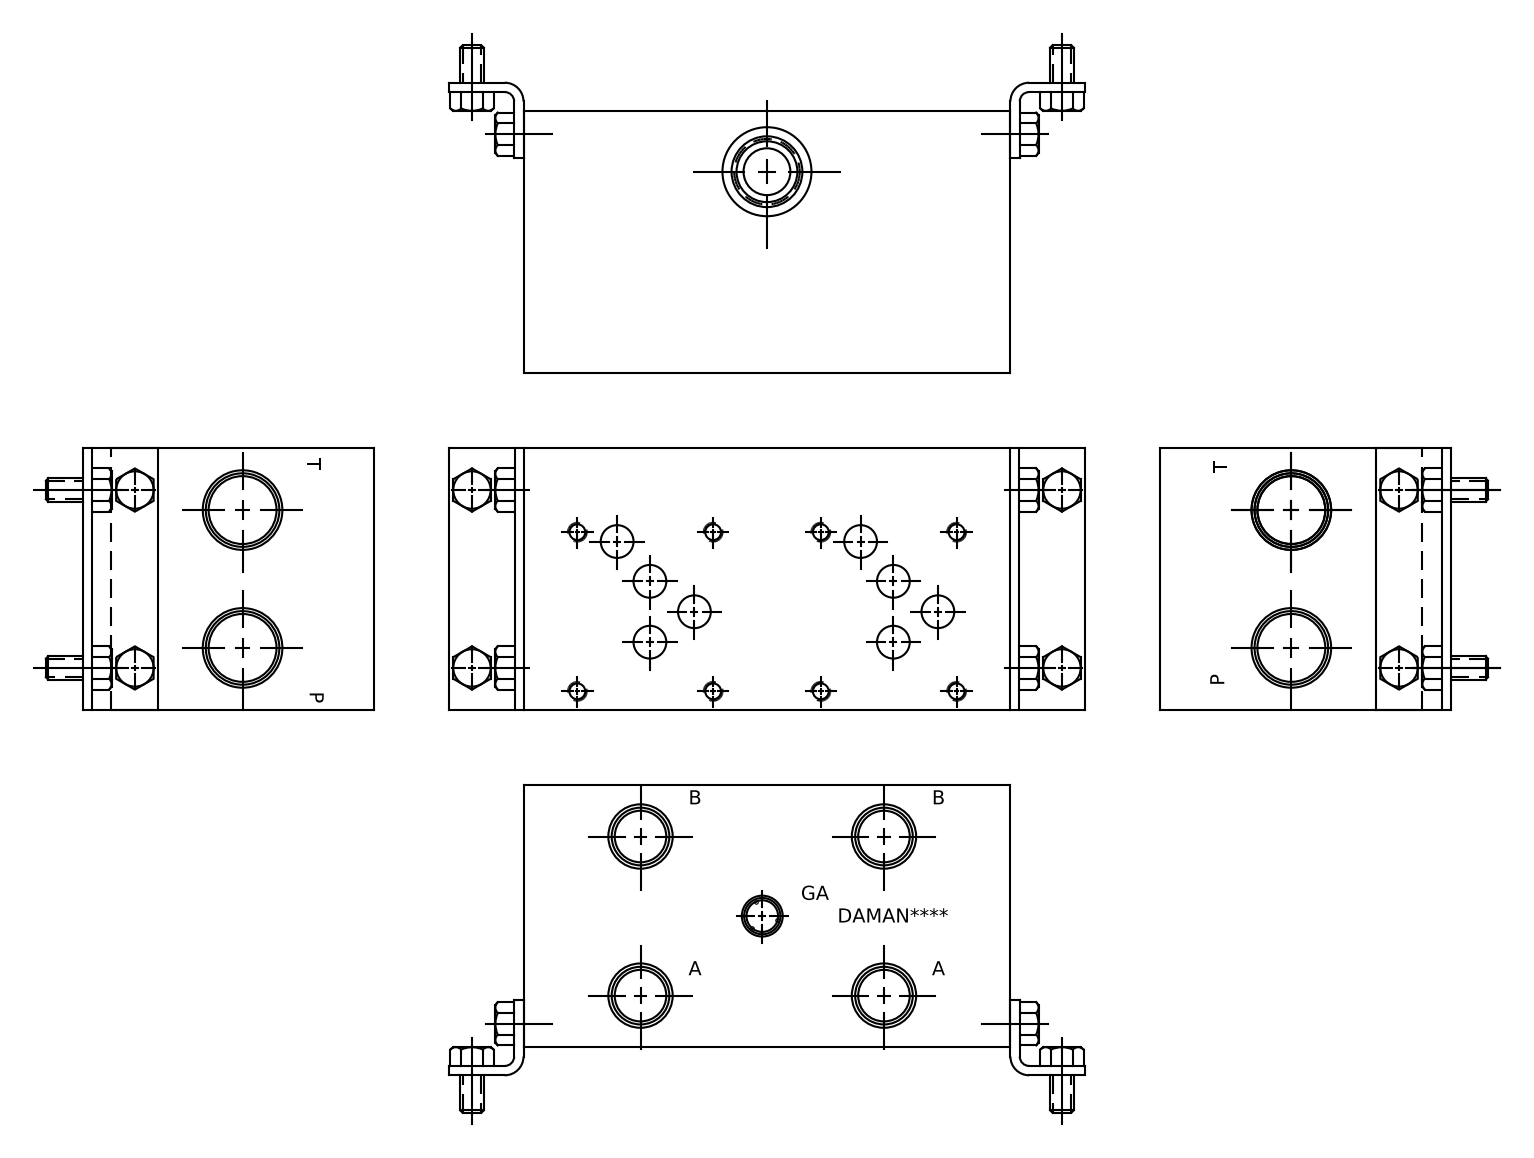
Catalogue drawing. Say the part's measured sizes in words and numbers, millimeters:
The part is named "Part_AD05P023P~C_3D". Its 3-D file was written by "Autodesk Inventor 2019 (AUTOMOTIVE_DESIGN)". It is 1 solid with 623 faces: 360 planar, 56 cylindrical and 207 other. Overall it measures 165.1 by 88.9 by 88.9 millimeters. Its volume is 1 213 000 cubic millimeters and its surface area 94 389 square millimeters. Round holes: 8 of diameter 5.11, 8 of diameter 6.35, 7 of diameter 11.13, 4 of diameter 17.48, 4 of diameter 21.59, 2 of diameter 6.53, 2 of diameter 7.92, 2 of diameter 23.01, 2 of diameter 26.92, 1 of diameter 10.72, 1 of diameter 11.11, 1 of diameter 13.87. The main face-to-face distances are 88.9, 165.1, 15.85, 149.25, 15.37, 73.53, 133.4, 88.11, 72.74, 0.79. The hole center spacings are 82.55, 46.05, 70.95, 43, 53.98, 98.63, 13.88, 18.27.
